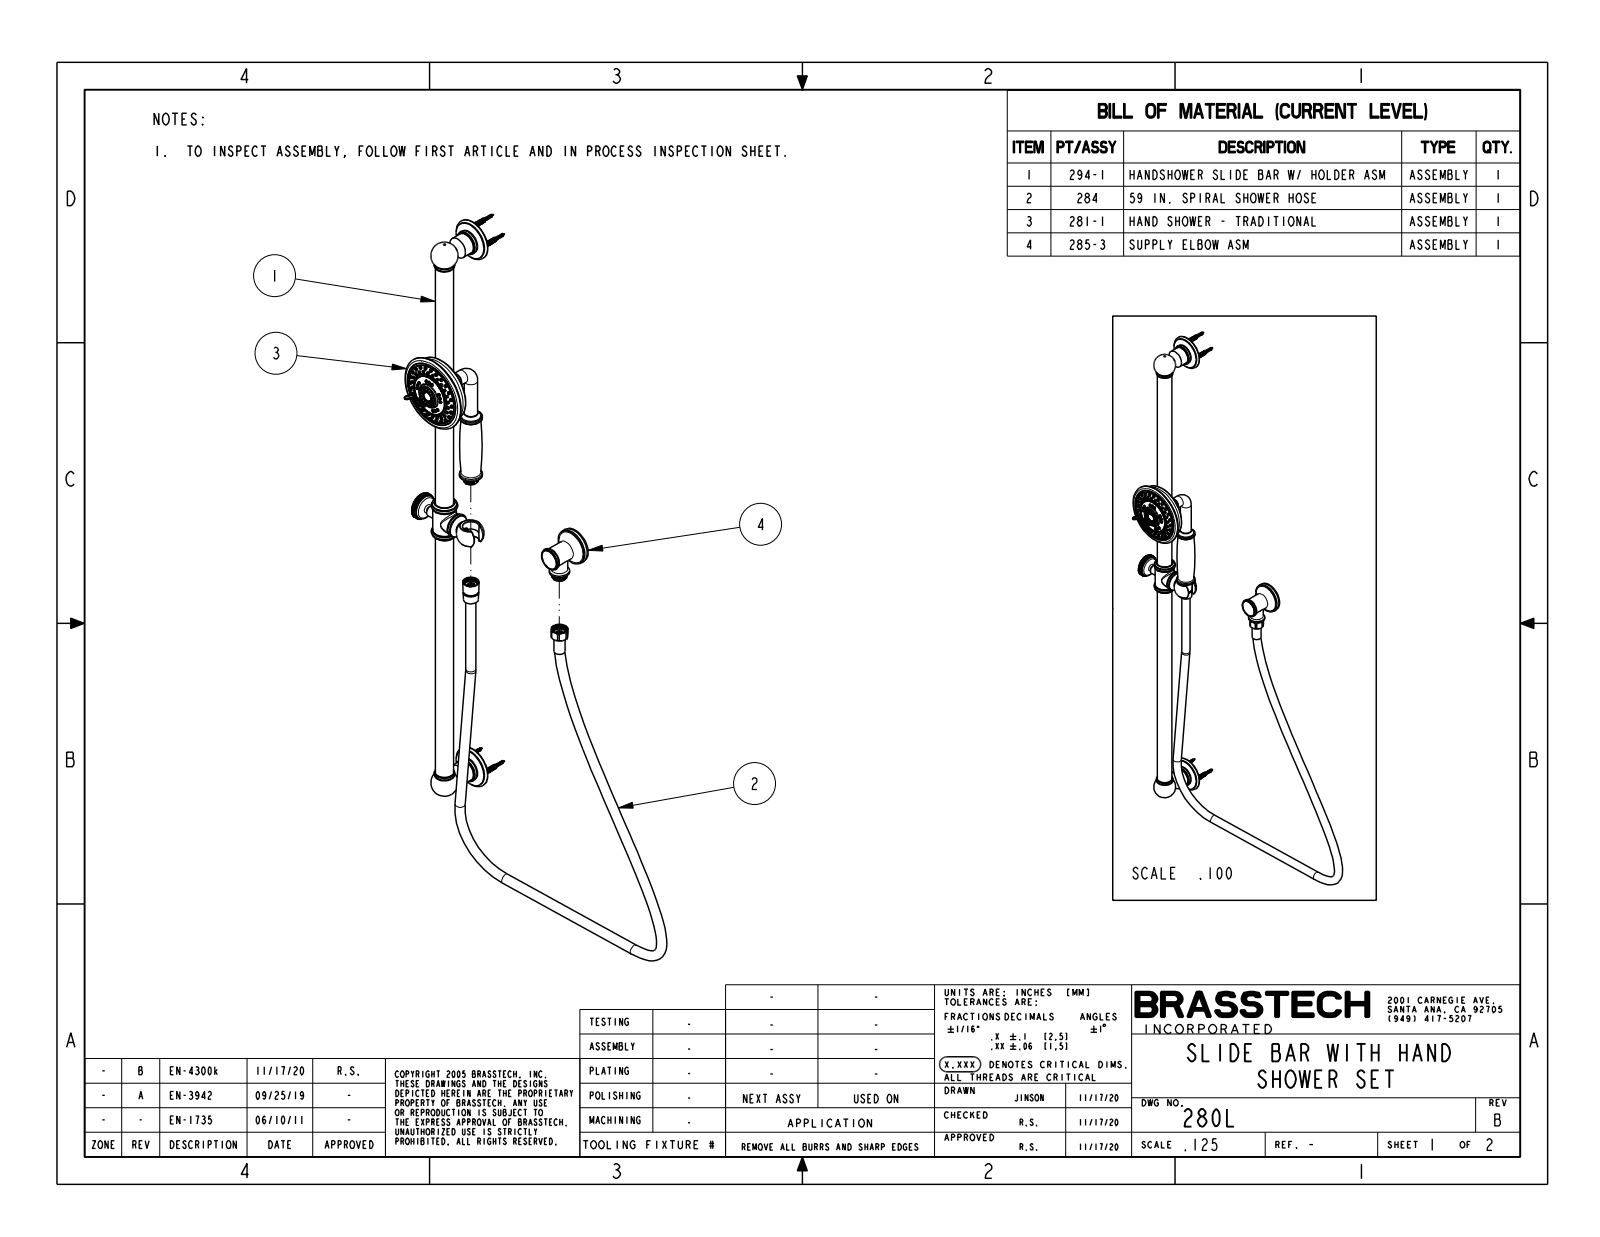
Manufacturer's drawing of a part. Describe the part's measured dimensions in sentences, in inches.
The part is named "280L". Its 3-D file was written by "CREO PARAMETRIC BY PTC INC, 2018400 (CONFIG_CONTROL_DESIGN)". It is 1 solid with 1602 faces: 343 planar, 370 cylindrical and 889 other. Overall it measures 38.889 by 17.117 by 5.745 inches. Its volume is 76.85 cubic inches and its surface area 351.1 square inches. Round holes: 1 of diameter 0.136, 1 of diameter 0.335, 1 of diameter 1.08. Round bosses or shafts: 39 of diameter 0.142, 23 of diameter 0.165, 3 of diameter 0.56, 2 of diameter 2.375, 2 of diameter 2.15, 2 of diameter 1.35, 2 of diameter 1.3, 2 of diameter 1.21. Partial cylindrical surfaces (rounded edges, fillets, slot ends): 4 of radius 0.02, 4 of radius 0.03, 1 of radius 0.138, 1 of radius 0.409, 1 of radius 0.472, 1 of radius 0.494, 1 of radius 0.512, 1 of radius 0.748. The main face-to-face distances are 0.55, 0.54, 0.593, 5.58, 5.57, 5.03, 0.595, 1.595, 0.12, 1.182.
